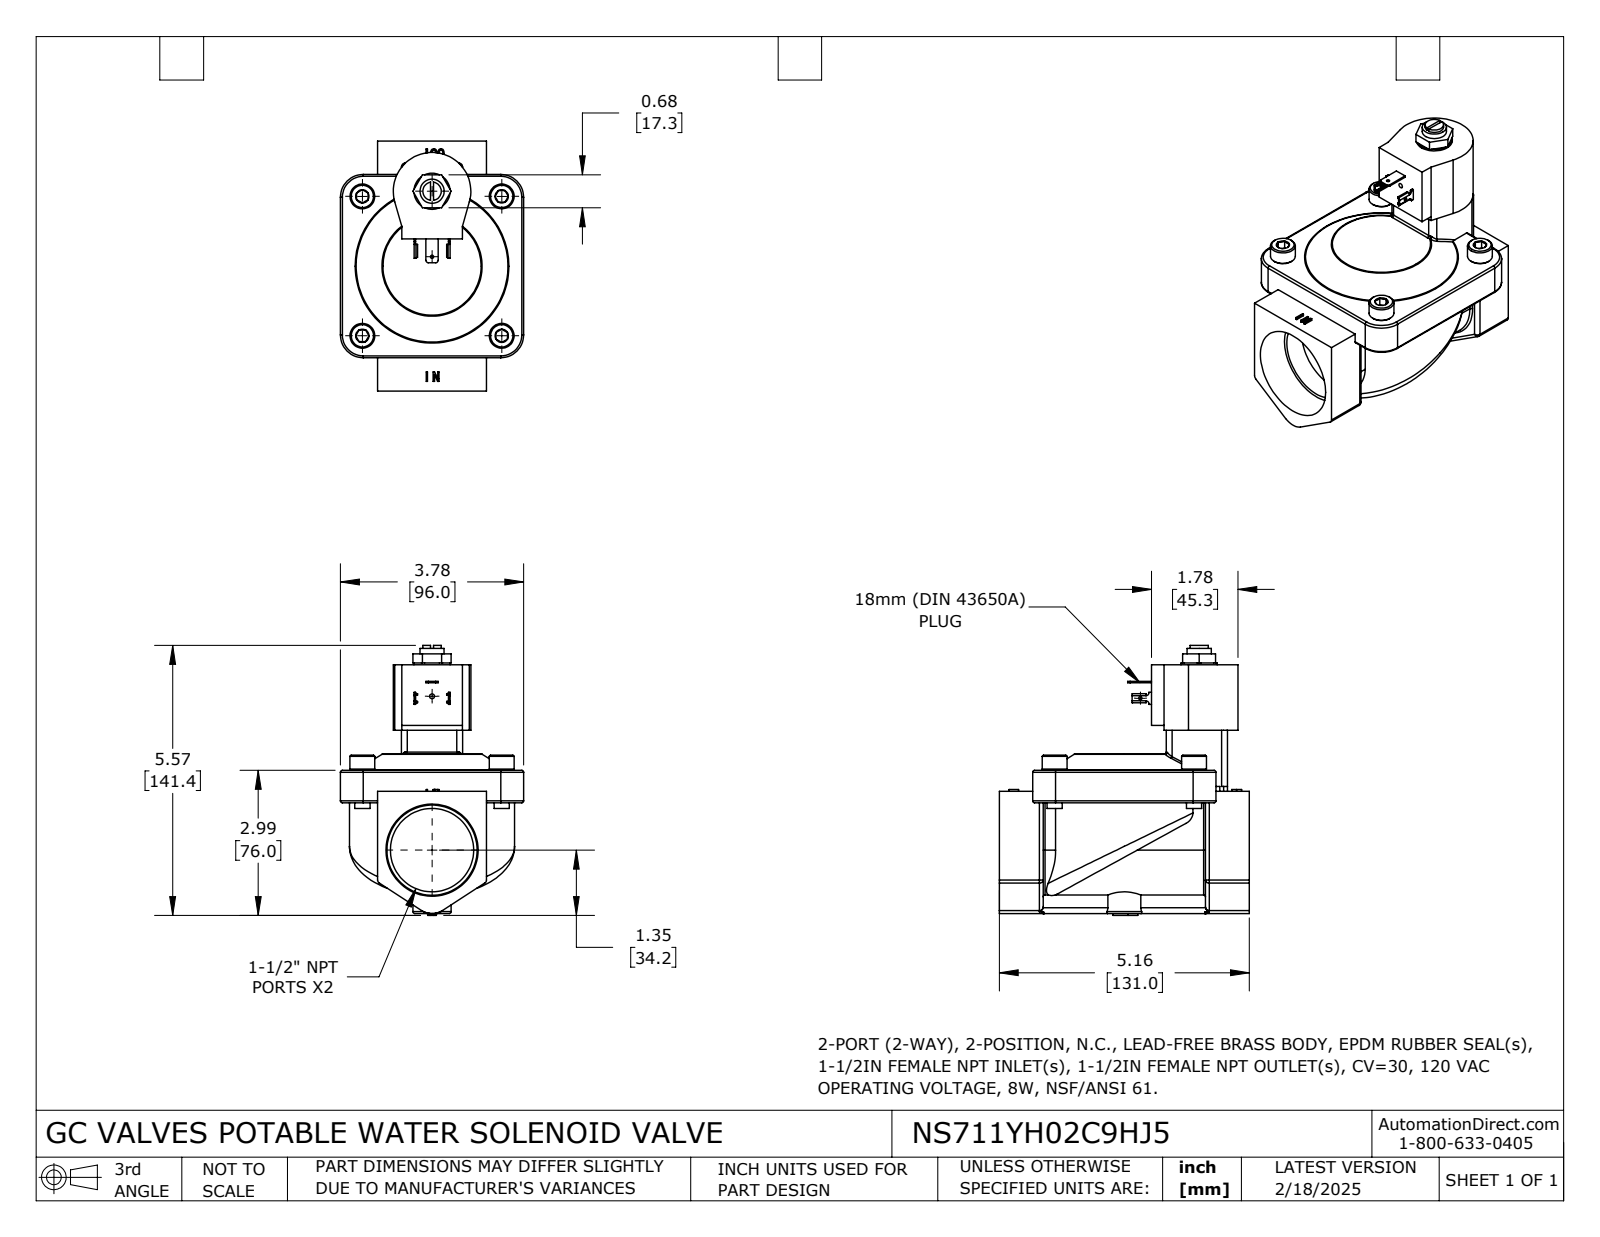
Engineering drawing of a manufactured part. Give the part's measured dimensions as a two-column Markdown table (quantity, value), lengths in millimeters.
| quantity | value |
| --- | --- |
| part name | NS711YH02C9HJ5 |
| STEP written by | SolidWorks 2024 (CONFIG_CONTROL_DESIGN) |
| units | millimeters |
| bodies | 1 solid, 442 faces (201 planar, 115 cylindrical, 126 other) |
| overall size | 141.37 × 131 × 96 |
| volume | 541 934 mm³ |
| surface area | 70 734 mm² |
| round holes (diameter × count) | 1.68 × 1, 1.7 × 1, 2.53 × 1, 30.48 × 1, 43.66 × 1 |
| round bosses / shafts (diameter × count) | 13 × 4, 8 × 4, 18.95 × 1, 12.67 × 1, 9.65 × 1 |
| partial cylindrical surfaces (radius × count) | 2 × 14, 1 × 13, 3 × 6, 0.15 × 4, 1.04 × 4, 12 × 4, 0.2 × 2, 1.27 × 2 |
| main face-to-face distances | 19.5, 32, 11, 6, 76.5, 8.5, 96, 17, 25.5, 12.5 |
| hole center spacings | 34.29, 80.56 |
